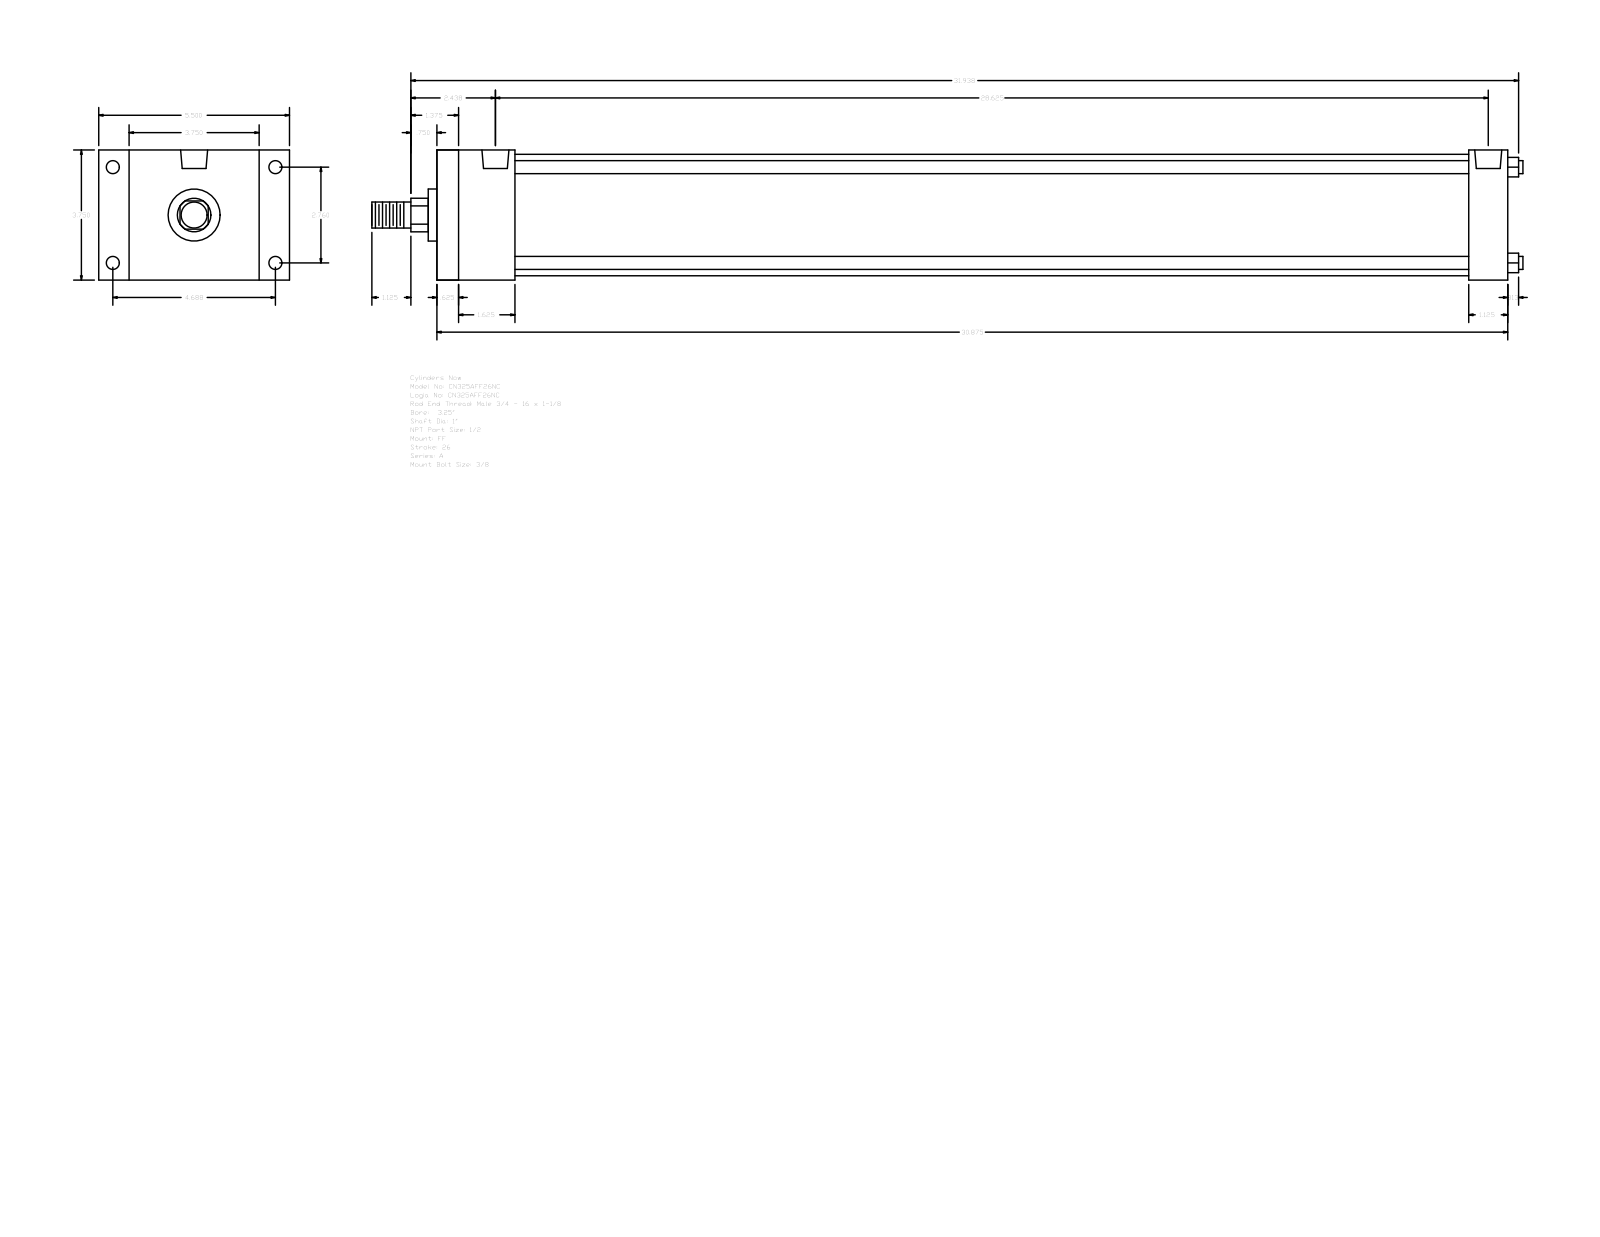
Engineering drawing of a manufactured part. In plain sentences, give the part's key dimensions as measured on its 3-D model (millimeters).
The part is named "A_FF__0325_1". Its 3-D file was written by "GSSL Pune (CONFIG_CONTROL_DESIGN)". It is 0 solids with 92 faces: 64 planar, 28 cylindrical and 0 other. Overall it measures 842.96 by 139.7 by 95.25 millimeters. Round holes: 4 of diameter 8.73, 4 of diameter 9.53, 2 of diameter 19.77. Round bosses or shafts: 4 of diameter 9.53, 1 of diameter 88.9, 1 of diameter 38.1, 1 of diameter 25.4, 1 of diameter 19.05. Partial cylindrical surfaces (rounded edges, fillets, slot ends): 1 of radius 12.29. The main face-to-face distances are 95.24, 784.22, 15.87, 768.35, 22.23, 117.47, 28.57, 57.15, 755.65, 41.28. The hole center spacings are 3.18, 70.1, 119.06, 138.16, 720.72, 723.9, 727.08.
